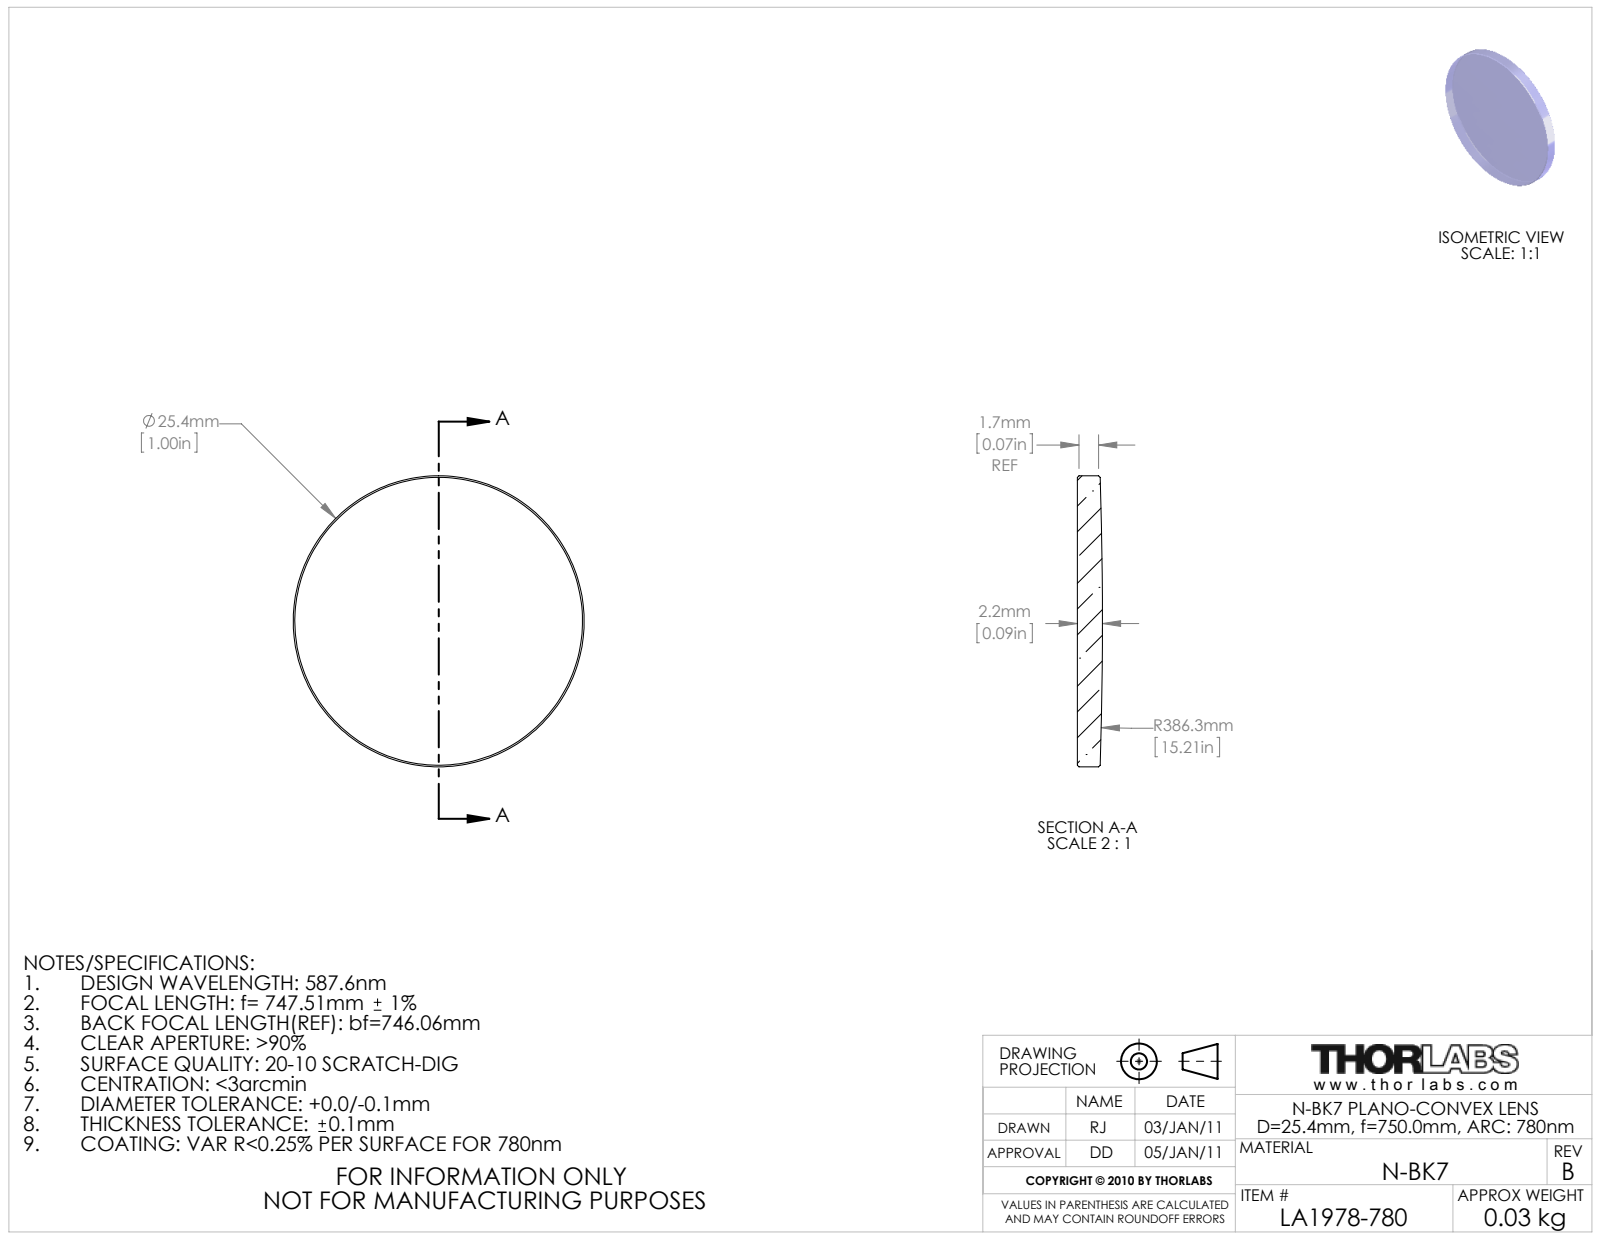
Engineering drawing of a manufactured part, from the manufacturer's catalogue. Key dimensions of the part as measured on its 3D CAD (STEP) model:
Part name (STEP PRODUCT): 21805-E0W
STEP written by: SolidWorks 2011 (AUTOMOTIVE_DESIGN)
Units: millimetres
Bodies: 0 solids, 9 faces (1 planar, 2 cylindrical, 6 other)
Overall size (bounding box): 25.4 × 25.4 × 2.2
Round bosses / shafts (diameter × count): ⌀25.4 ×1
